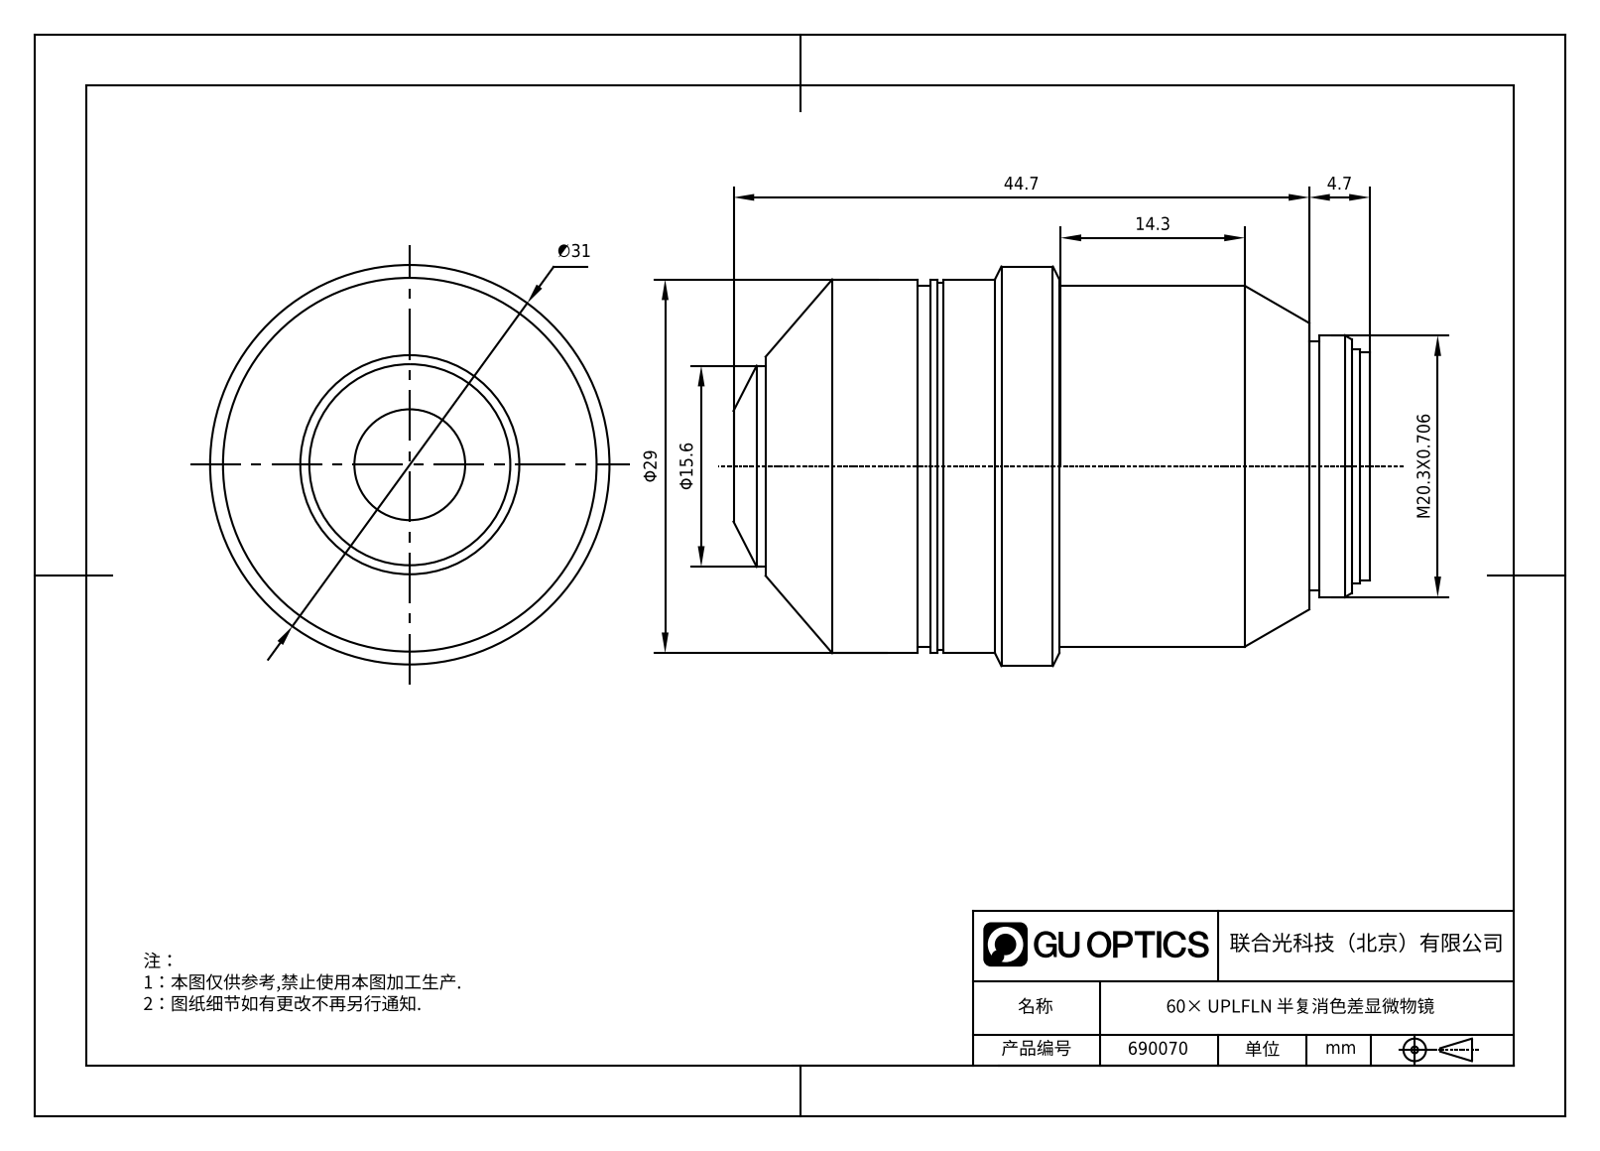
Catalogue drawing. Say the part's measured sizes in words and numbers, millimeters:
The part is named "690070". Its 3-D file was written by "SolidWorks 2020 (CONFIG_CONTROL_DESIGN)". It is 1 solid with 48 faces: 12 planar, 24 cylindrical and 12 other. Overall it measures 49.39 by 31 by 31 millimeters. Its volume is 27 303 cubic millimeters and its surface area 5 221 square millimeters. Round bosses or shafts: 1 of diameter 31, 1 of diameter 29, 1 of diameter 28.5, 1 of diameter 28, 1 of diameter 20.32, 1 of diameter 19.32, 1 of diameter 18.18, 1 of diameter 17.68. The main face-to-face distances are 4.7, 1, 44.69, 49.39, 0.5, 14.29, 15.29, 30.4, 35.1, 29.4.
